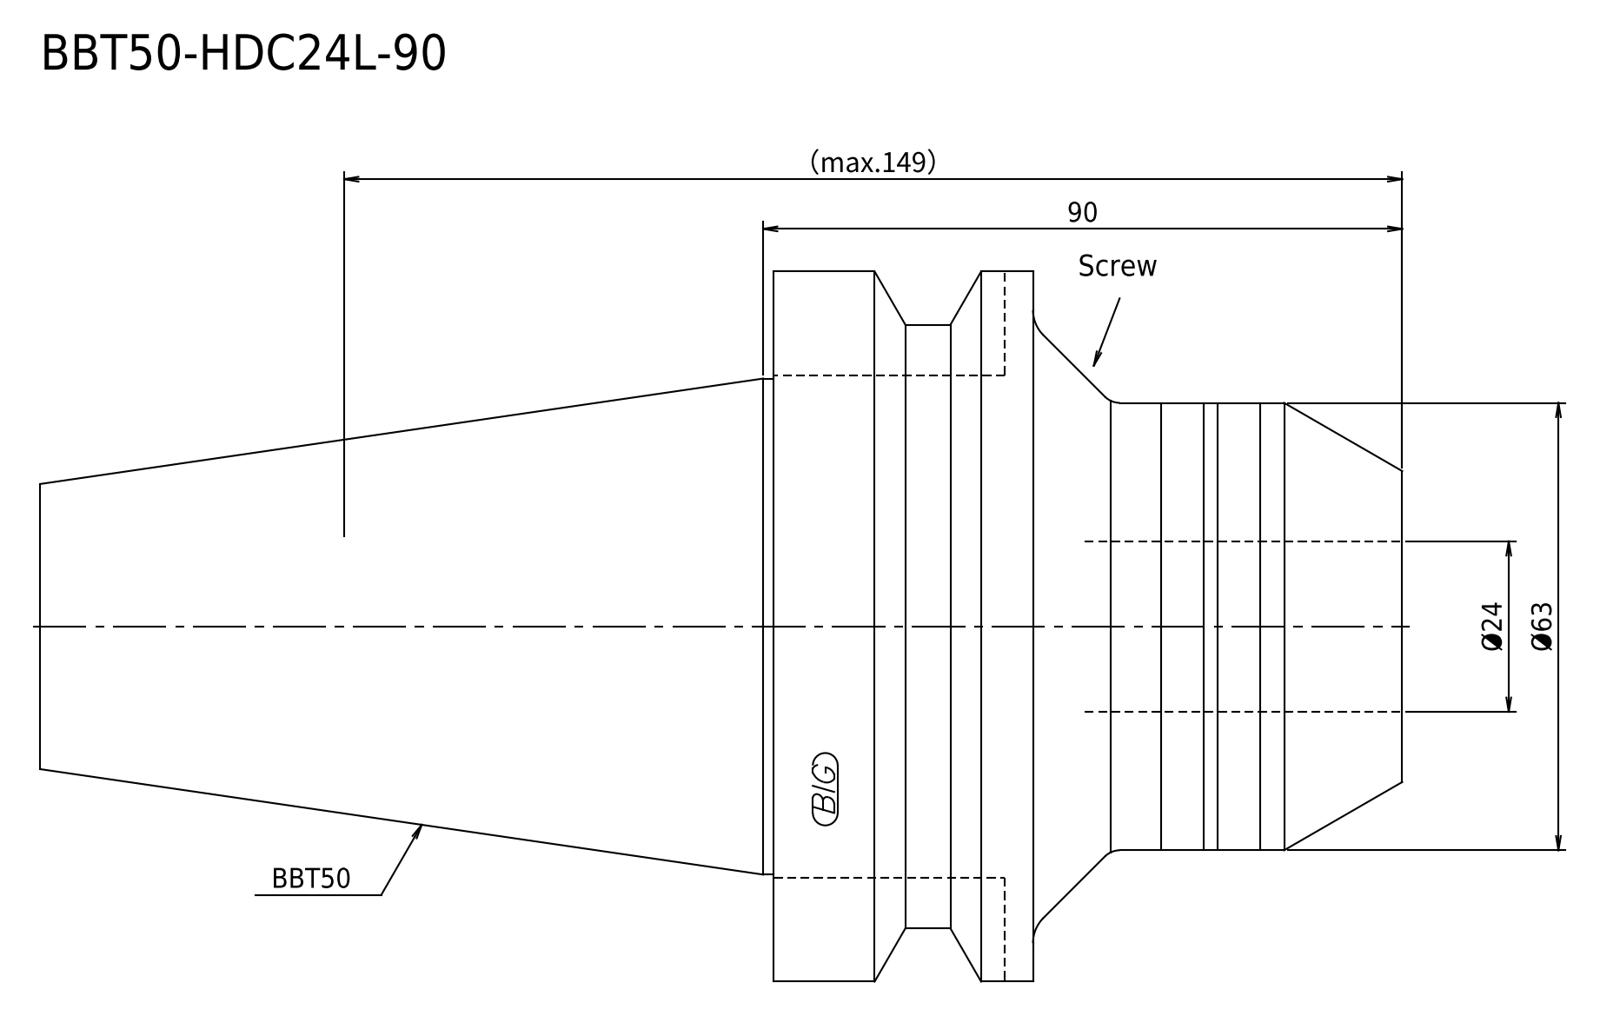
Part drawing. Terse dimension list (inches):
written by: Kubotek KeyCreator V8.5.1 (14335) (CONFIG_CONTROL_DESIGN)
unit: in
bodies: 1 solid, 18 faces (5 planar, 5 cylindrical, 8 other)
size: 7.551 × 3.937 × 3.937
volume: 41.37 in³; area: 80.72 in²
bosses: 1× ⌀3.937, 1× ⌀3.346, 1× ⌀2.75, 1× ⌀2.48
face distances: 1.437, 5.504, 4.067, 2.02, 3.457, 7.524, 0.028, 2.047, 3.484, 7.551
